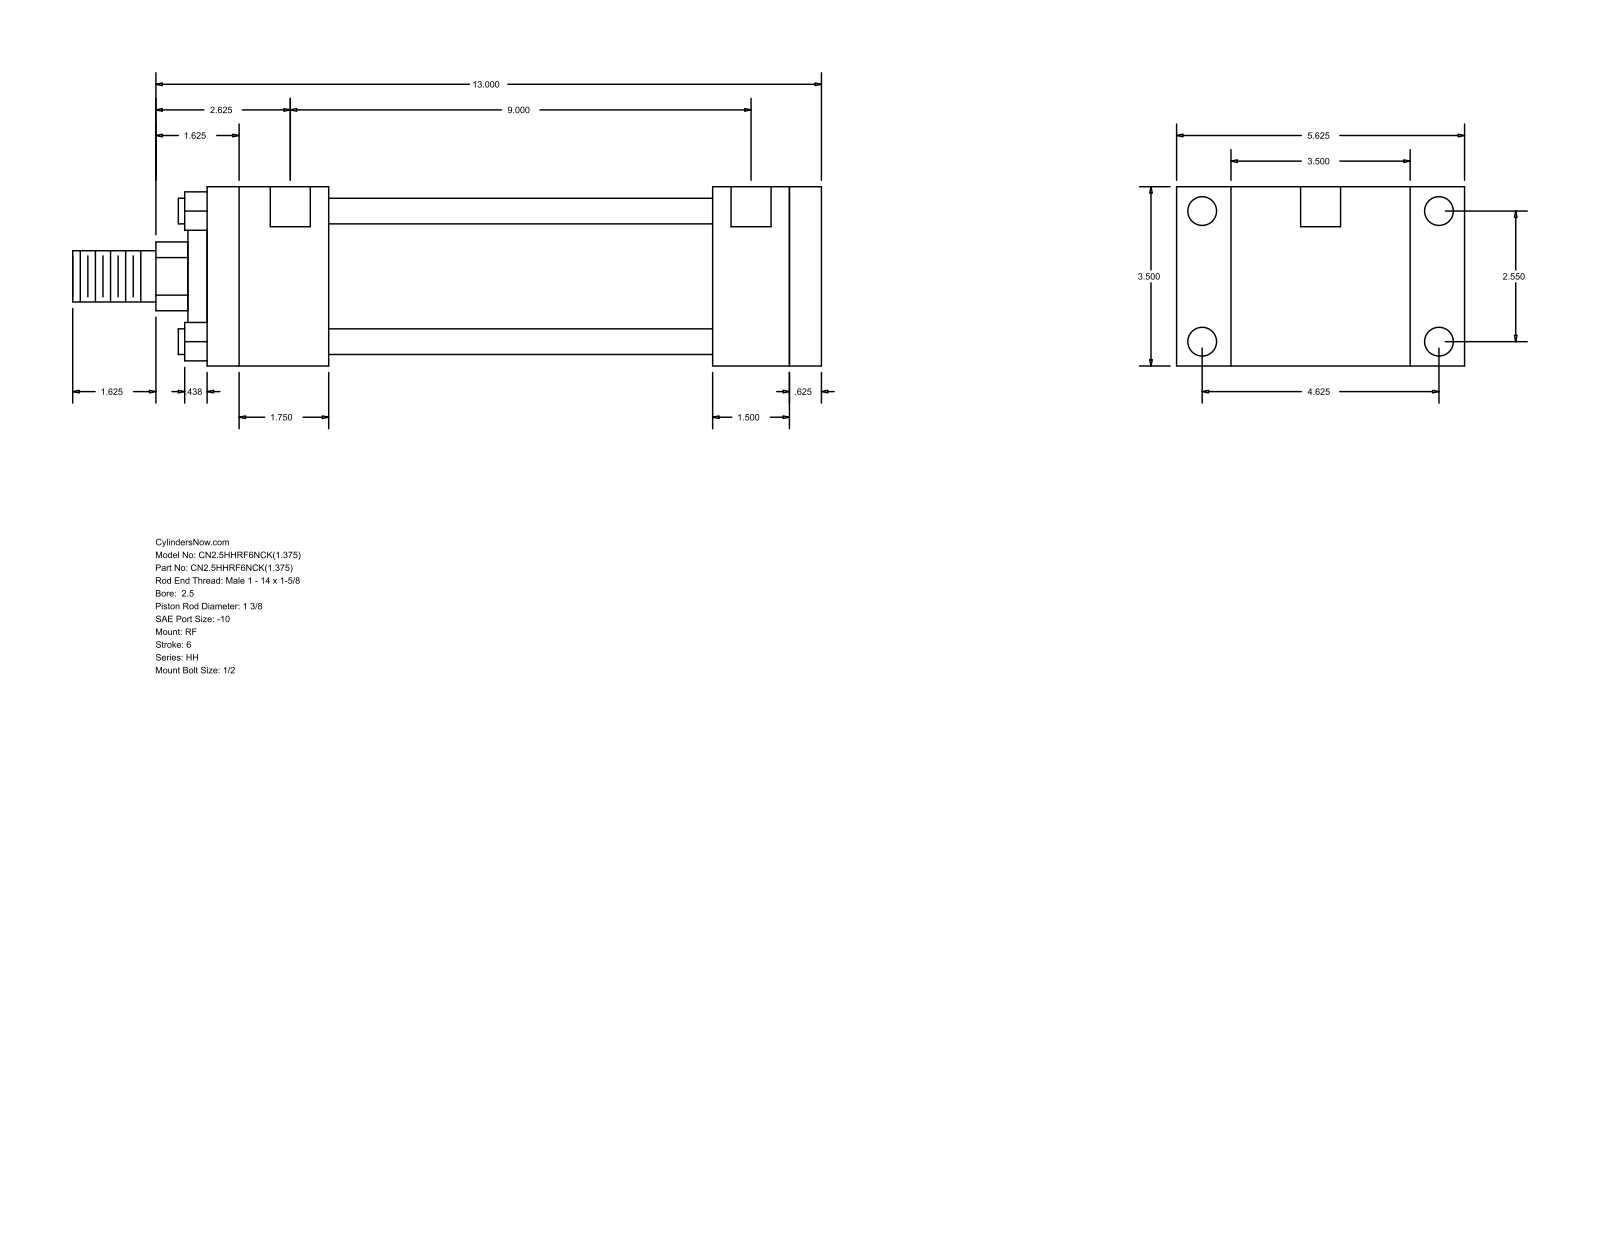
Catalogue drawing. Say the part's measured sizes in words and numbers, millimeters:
The part is named "HH_RF__0250_1.375". Its 3-D file was written by "GSSL Pune (CONFIG_CONTROL_DESIGN)". It is 0 solids with 92 faces: 64 planar, 28 cylindrical and 0 other. Overall it measures 371.48 by 142.88 by 88.9 millimeters. Round holes: 4 of diameter 5.56, 4 of diameter 14.3, 2 of diameter 19.84. Round bosses or shafts: 4 of diameter 12.7, 1 of diameter 73.03, 1 of diameter 50.8, 1 of diameter 34.92, 1 of diameter 25.4. Partial cylindrical surfaces (rounded edges, fillets, slot ends): 1 of radius 17.06. The main face-to-face distances are 88.9, 304.8, 15.88, 288.92, 53.97, 60.32, 228.6, 244.48, 250.83, 190.51. The hole center spacings are 64.76, 117.48, 134.15, 231.77, 1.58, 1.59, 228.6, 230.18.
